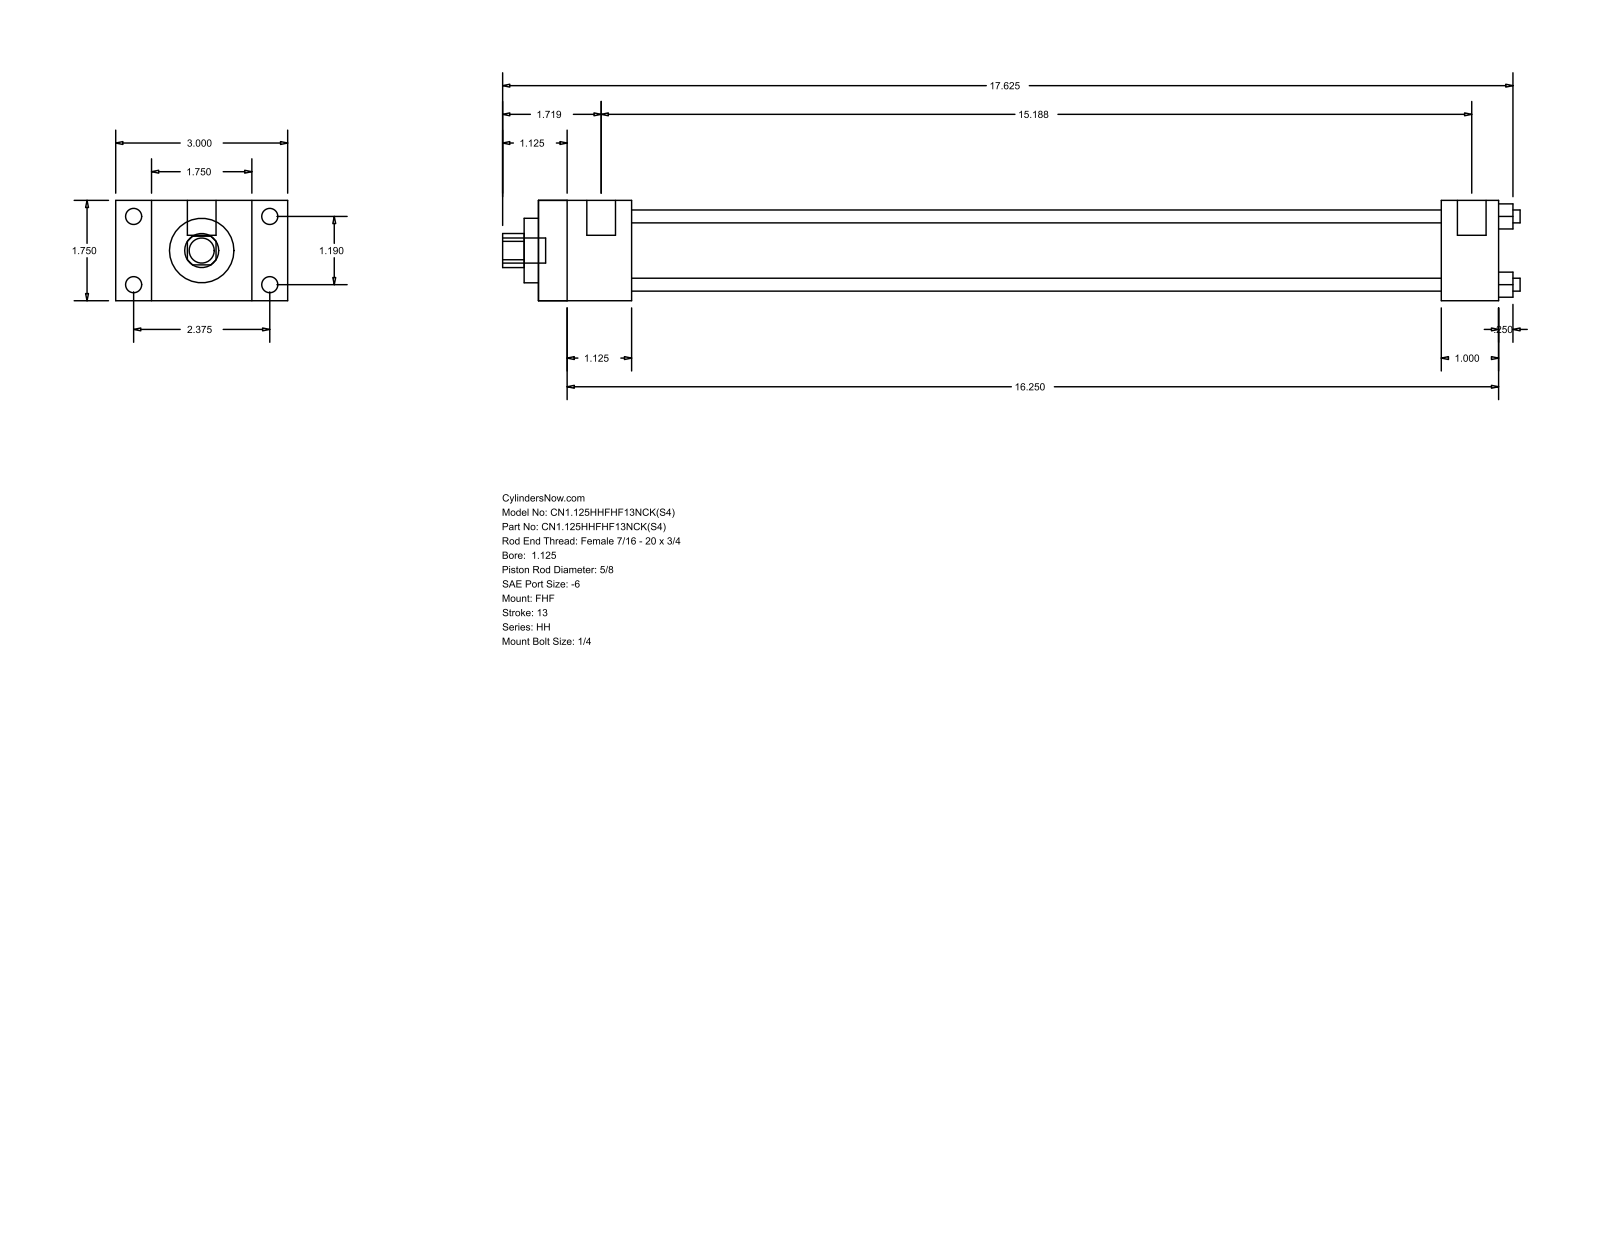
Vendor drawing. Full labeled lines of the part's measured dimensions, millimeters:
Part name (STEP PRODUCT): HH_FHF__0112_0.625
STEP written by: GSSL Pune (CONFIG_CONTROL_DESIGN)
Units: millimetres
Bodies: 0 solids, 88 faces (60 planar, 28 cylindrical, 0 other)
Overall size (bounding box): 450.85 × 76.2 × 44.45
Round holes (diameter × count): ⌀5.71 ×4, ⌀15.88 ×1, ⌀28.57 ×1, ⌀34.92 ×1
Round bosses / shafts (diameter × count): ⌀7.14 ×4, ⌀5.56 ×4, ⌀12.7 ×2, ⌀11.11 ×1
Partial cylindrical surfaces — rounded edges, fillets, slot ends (radius × count): R7.54 ×1
Main face-to-face distances: 44.46, 15.87, 60.33, 41.27, 76.2, 425.44, 384.17, 400.05, 358.78, 25.39
Hole centre spacings: 21.37, 30.22, 42.74
